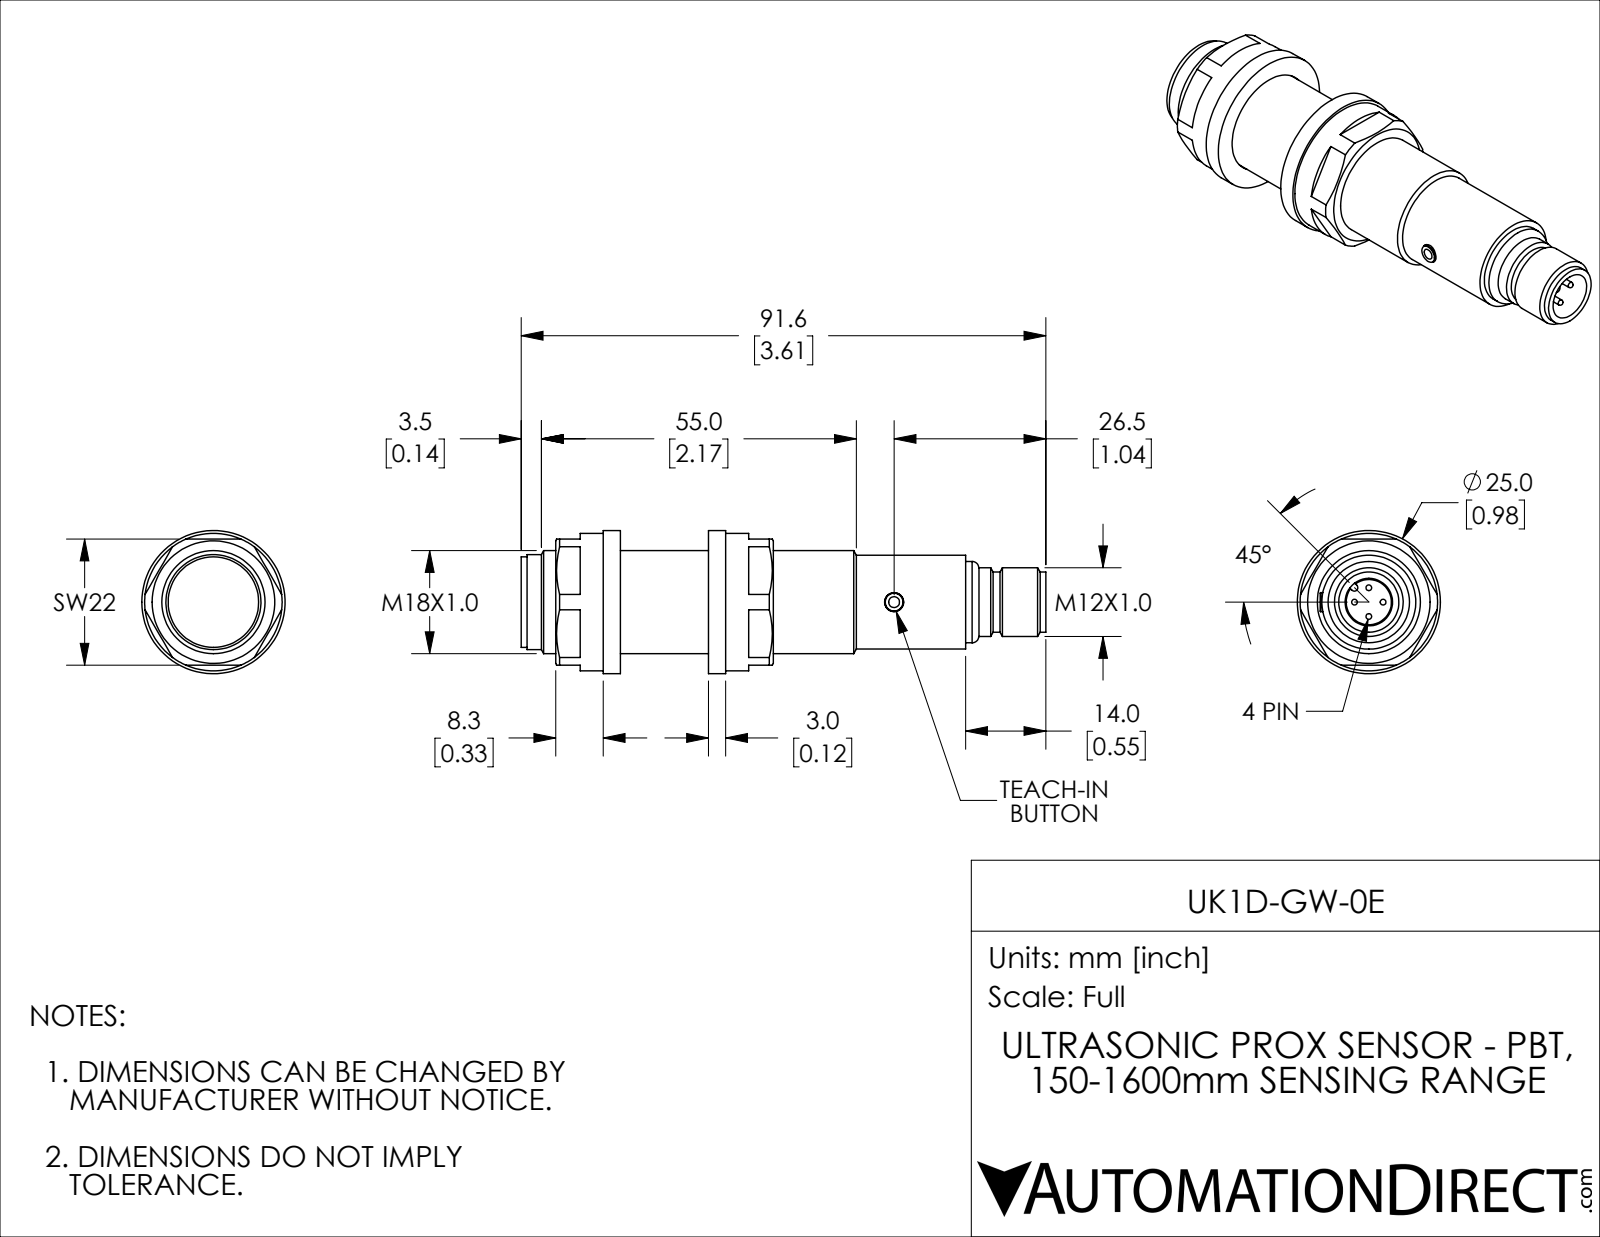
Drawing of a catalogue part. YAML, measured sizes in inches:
part_name: "UK1D-GW-0E"
step_written_by: "SolidWorks 2018 (AUTOMOTIVE_DESIGN)"
units: inches
bodies: {solids: 6, faces: 123, planar: 43, cylindrical: 49, other: 31}
overall_size: [3.606, 0.984, 0.984]
volume: 1.477
surface_area: 16.01
round_holes:
  - {diameter: 0.13, count: 1}
  - {diameter: 0.327, count: 1}
  - {diameter: 0.709, count: 1}
  - {diameter: 0.717, count: 1}
round_bosses_or_shafts:
  - {diameter: 0.039, count: 4}
  - {diameter: 0.984, count: 1}
  - {diameter: 0.945, count: 1}
  - {diameter: 0.654, count: 1}
  - {diameter: 0.646, count: 1}
  - {diameter: 0.622, count: 1}
  - {diameter: 0.559, count: 1}
  - {diameter: 0.472, count: 1}
partial_cylinders:
  - {radius: 0.024, count: 1}
face_to_face_distances: [0.118, 0.724, 0.843, 0.606, 0.866, 0.327, 0.445, 1.051, 1.169, 0.563]
